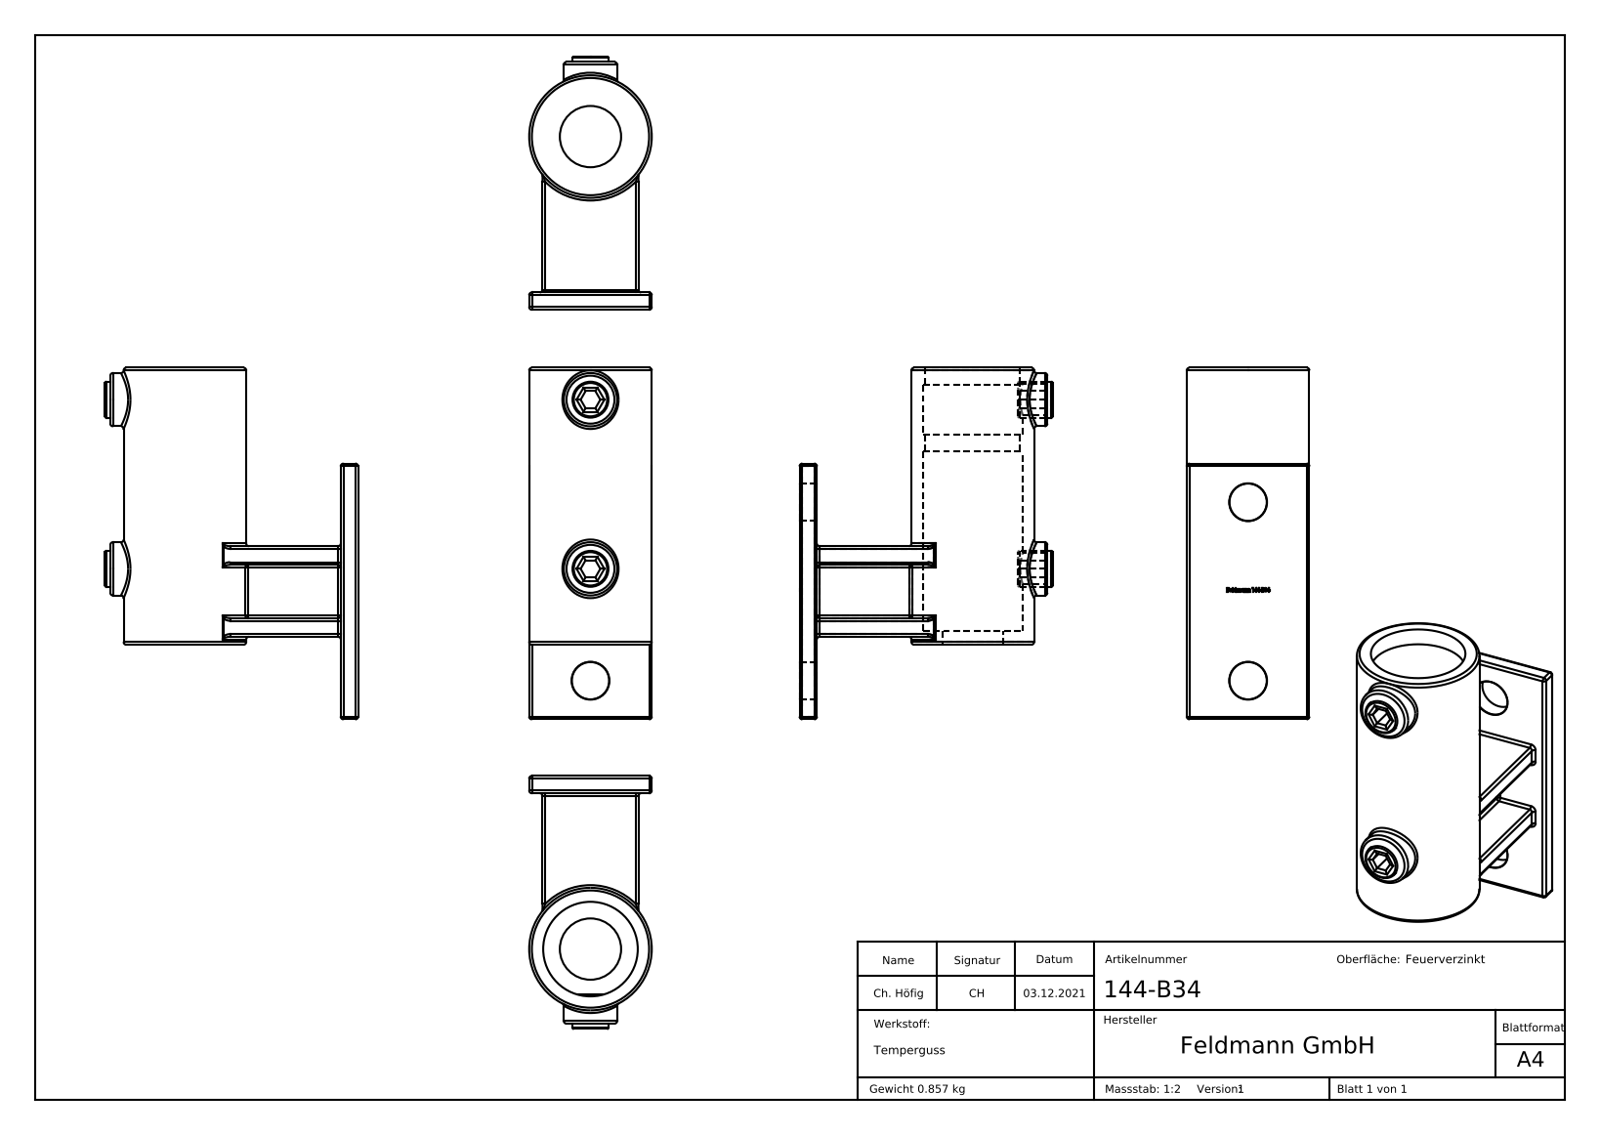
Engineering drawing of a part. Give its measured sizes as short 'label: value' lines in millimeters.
name: 144-B34 Teil 1; 144-B34 Teil 2; 144-B34; 144-B34 Teil 1_144-B34 Teil 1
written by: SolidWorks 2018 (CONFIG_CONTROL_DESIGN)
unit: mm
bodies: 3 solids, 391 faces (180 planar, 80 cylindrical, 131 other)
size: 132 × 95 × 46
volume: 117 117 mm³; area: 49 203 mm²
holes: 2× ⌀11.8, 2× ⌀14, 1× ⌀23, 1× ⌀35.5, 1× ⌀37.5
bosses: 2× ⌀20, 2× ⌀13.5, 1× ⌀46
rounds: 36× R1, 24× R2
face distances: 6.5, 5, 7, 27, 20, 34, 3, 37, 10, 30
hole spacings: 25, 38.5, 42, 63.5, 67, 105.5
